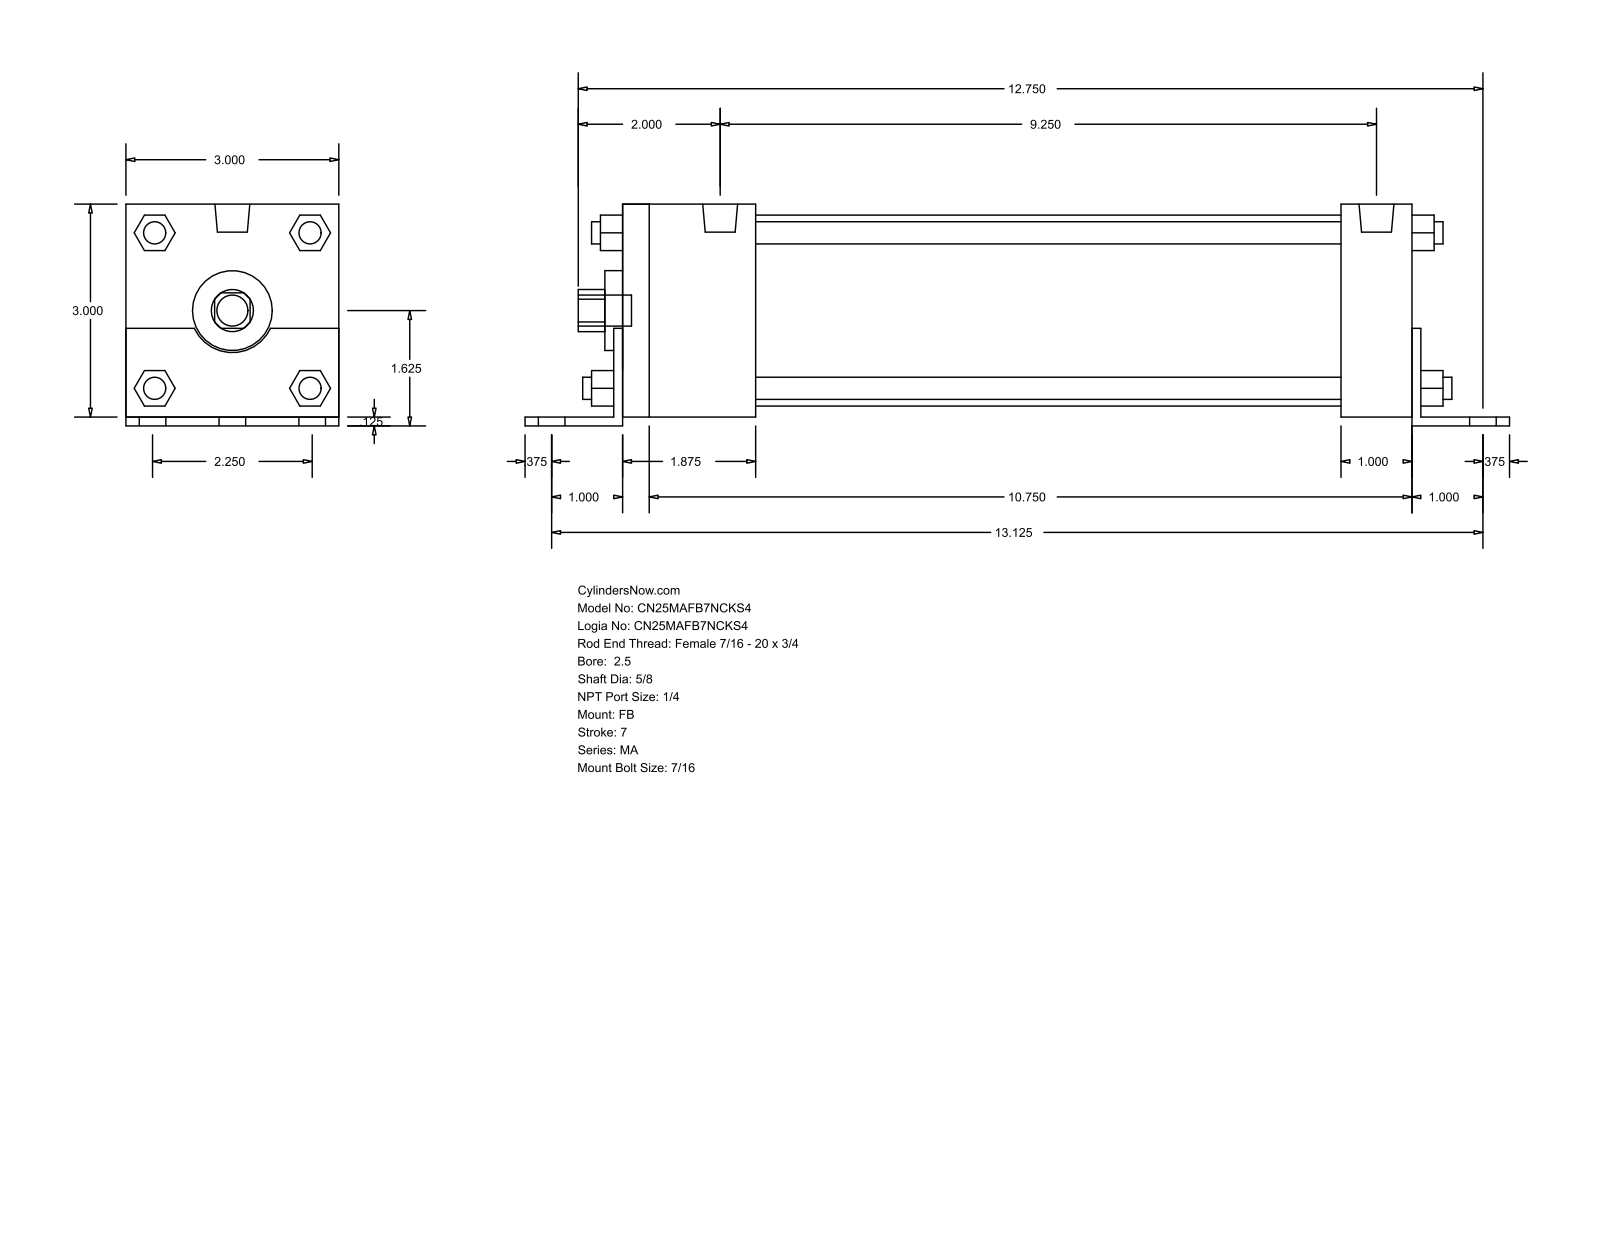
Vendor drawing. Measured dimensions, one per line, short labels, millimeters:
name: MA_FB__0250_0.625
written by: GSSL Pune (CONFIG_CONTROL_DESIGN)
unit: mm
bodies: 0 solids, 140 faces (105 planar, 35 cylindrical, 0 other)
size: 352.43 × 79.38 × 76.2
holes: 1× ⌀15.88, 1× ⌀28.57, 1× ⌀68.33
bosses: 8× ⌀7.94, 7× ⌀11.11, 2× ⌀12.49
rounds: 1× R7.54, 1× R15.05
face distances: 76.2, 3.17, 79.37, 282.57, 288.92, 3.18, 285.74, 47.62, 25.4, 285.75
